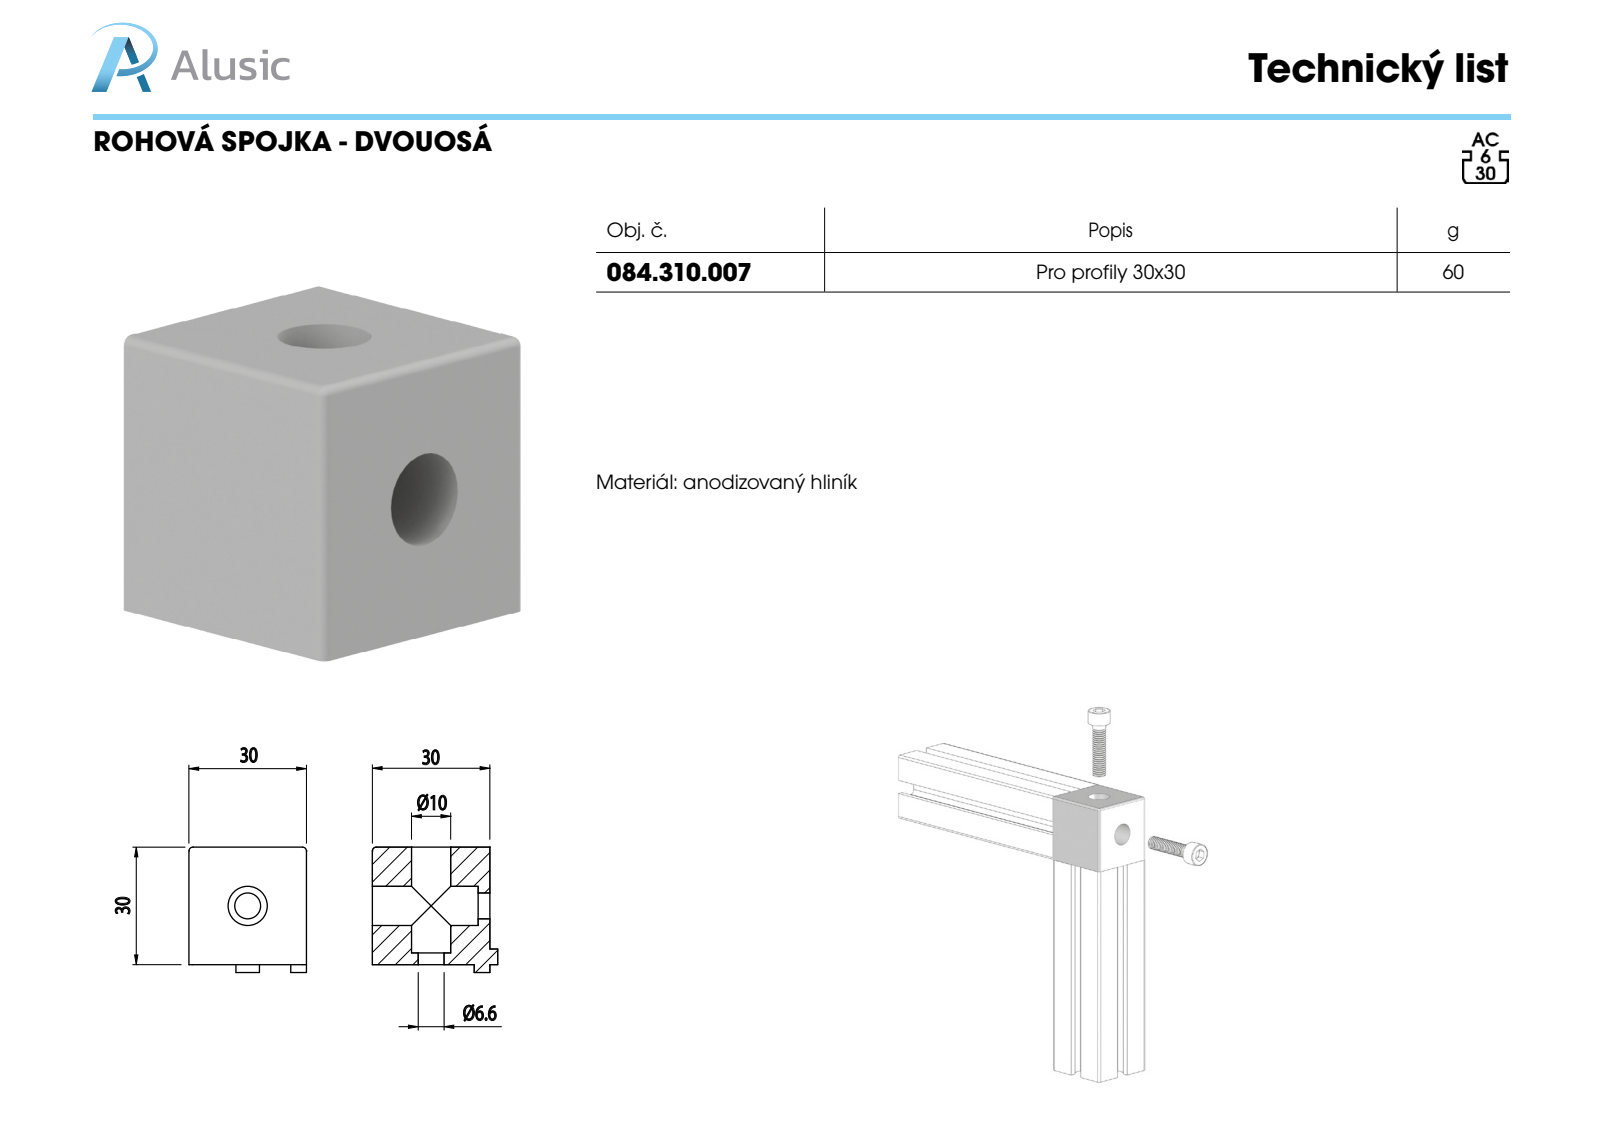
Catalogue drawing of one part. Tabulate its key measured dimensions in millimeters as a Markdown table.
| quantity | value |
| --- | --- |
| part name | 084.310.007 |
| STEP written by | SolidWorks 2011 (CONFIG_CONTROL_DESIGN) |
| units | millimeters |
| bodies | 1 solid, 45 faces (26 planar, 17 cylindrical, 2 other) |
| overall size | 32 × 32 × 30 |
| volume | 23 380 mm³ |
| surface area | 6 778 mm² |
| round holes (diameter × count) | 6.6 × 2, 10 × 2 |
| partial cylindrical surfaces (radius × count) | 1 × 5 |
| main face-to-face distances | 30, 2, 32, 5, 3, 27, 12, 18, 6, 14 |
